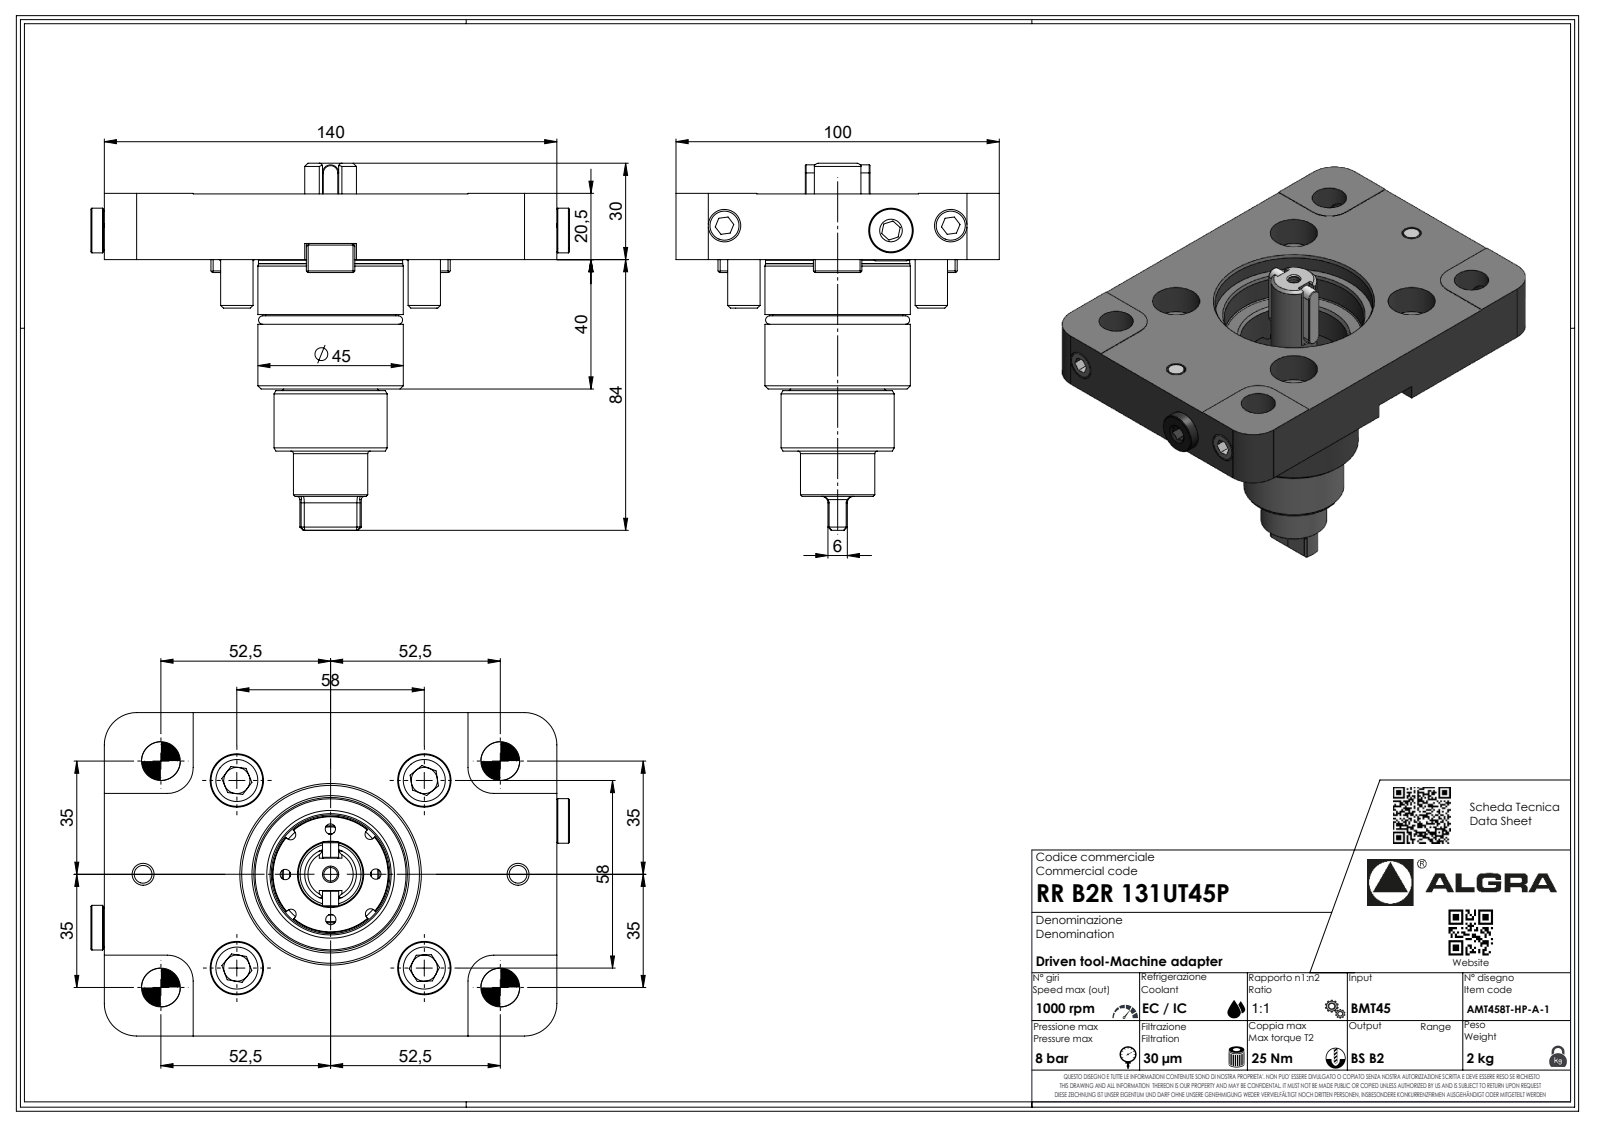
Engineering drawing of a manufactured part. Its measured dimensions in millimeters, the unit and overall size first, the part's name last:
Units: millimetres
Overall size (bounding box): 140 × 113.5 × 100
Round holes (diameter × count): ⌀2.1 ×1
Round bosses / shafts (diameter × count): ⌀45 ×1, ⌀44.6 ×1, ⌀40.2 ×1, ⌀35 ×1, ⌀23 ×1, ⌀16 ×1, ⌀6.37 ×1, ⌀1.7 ×1
Partial cylindrical surfaces — rounded edges, fillets, slot ends (radius × count): R2.5 ×12, R0.33 ×7, R0.52 ×7, R3.7 ×7, R2 ×6, R9.5 ×5, R3 ×4, R8 ×4
Main face-to-face distances: 20.3, 20.5, 100, 140, 40, 13, 45, 5, 60.3, 60.5
Volume: 373 347 mm³ · Surface area: 50 761 mm²
Bodies: 1 solid, 493 faces (327 planar, 82 cylindrical, 84 other)
Part name (STEP PRODUCT): RRB2R131UT45P
STEP written by: SolidWorks 2023 (AUTOMOTIVE_DESIGN)
